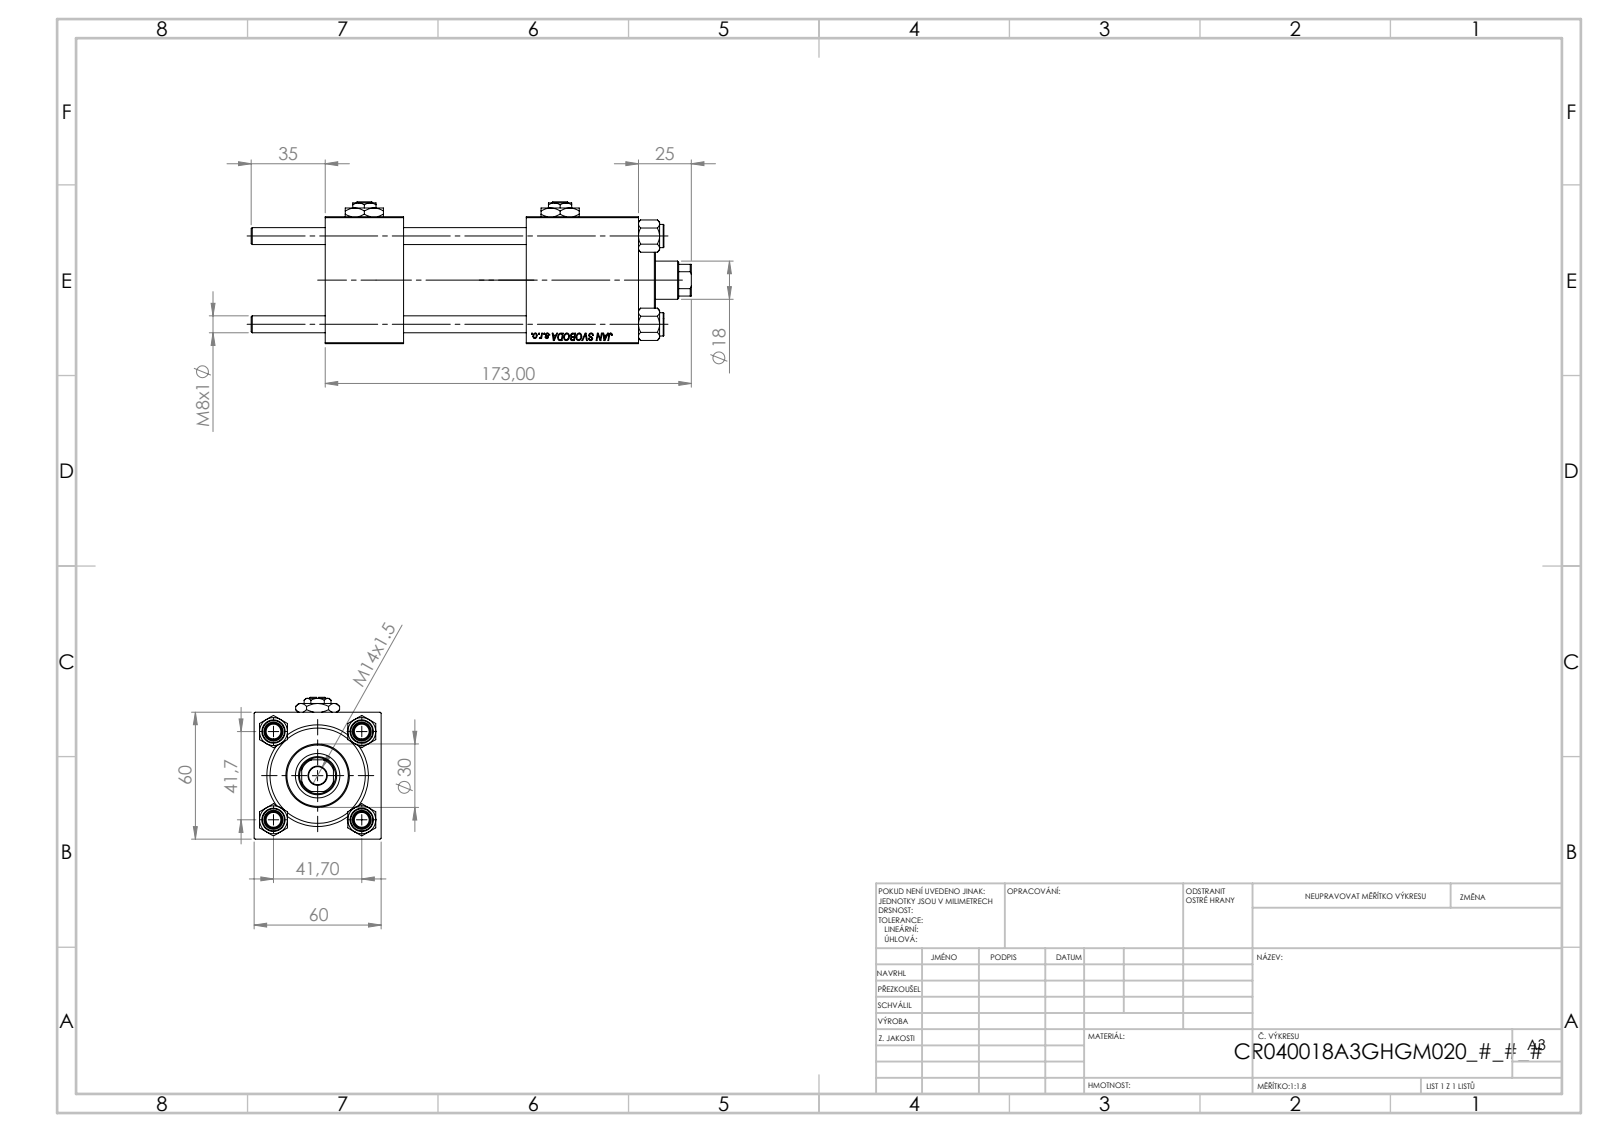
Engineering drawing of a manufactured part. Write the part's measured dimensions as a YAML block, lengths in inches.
part_name: "V215_VC_A; NUT_M5; CR025_012_A_0_G_A_G_M_020_+#_##_TYCINKA; V215CR_BODY_A (+2 more)"
step_written_by: "SolidWorks 2019 (CONFIG_CONTROL_DESIGN)"
units: inches
bodies: {solids: 13, faces: 1235, planar: 569, cylindrical: 88, other: 578}
overall_size: [8.189, 2.638, 2.362]
volume: 25.06
surface_area: 181.2
round_holes:
  - {diameter: 0.315, count: 4}
  - {diameter: 0.276, count: 2}
  - {diameter: 0.656, count: 2}
  - {diameter: 0.945, count: 2}
  - {diameter: 0.335, count: 1}
  - {diameter: 0.709, count: 1}
  - {diameter: 0.827, count: 1}
  - {diameter: 1.22, count: 1}
  - {diameter: 1.575, count: 1}
  - {diameter: 1.772, count: 1}
round_bosses_or_shafts:
  - {diameter: 0.433, count: 4}
  - {diameter: 1.811, count: 1}
  - {diameter: 1.181, count: 1}
partial_cylinders:
  - {radius: 0.335, count: 1}
face_to_face_distances: [2.362, 1.457, 5.827, 4.37, 2.283, 2.087, 3.74, 4.697, 3.24, 0.957]
hole_center_spacings: [1.161, 1.642, 2.322, 3.642]
